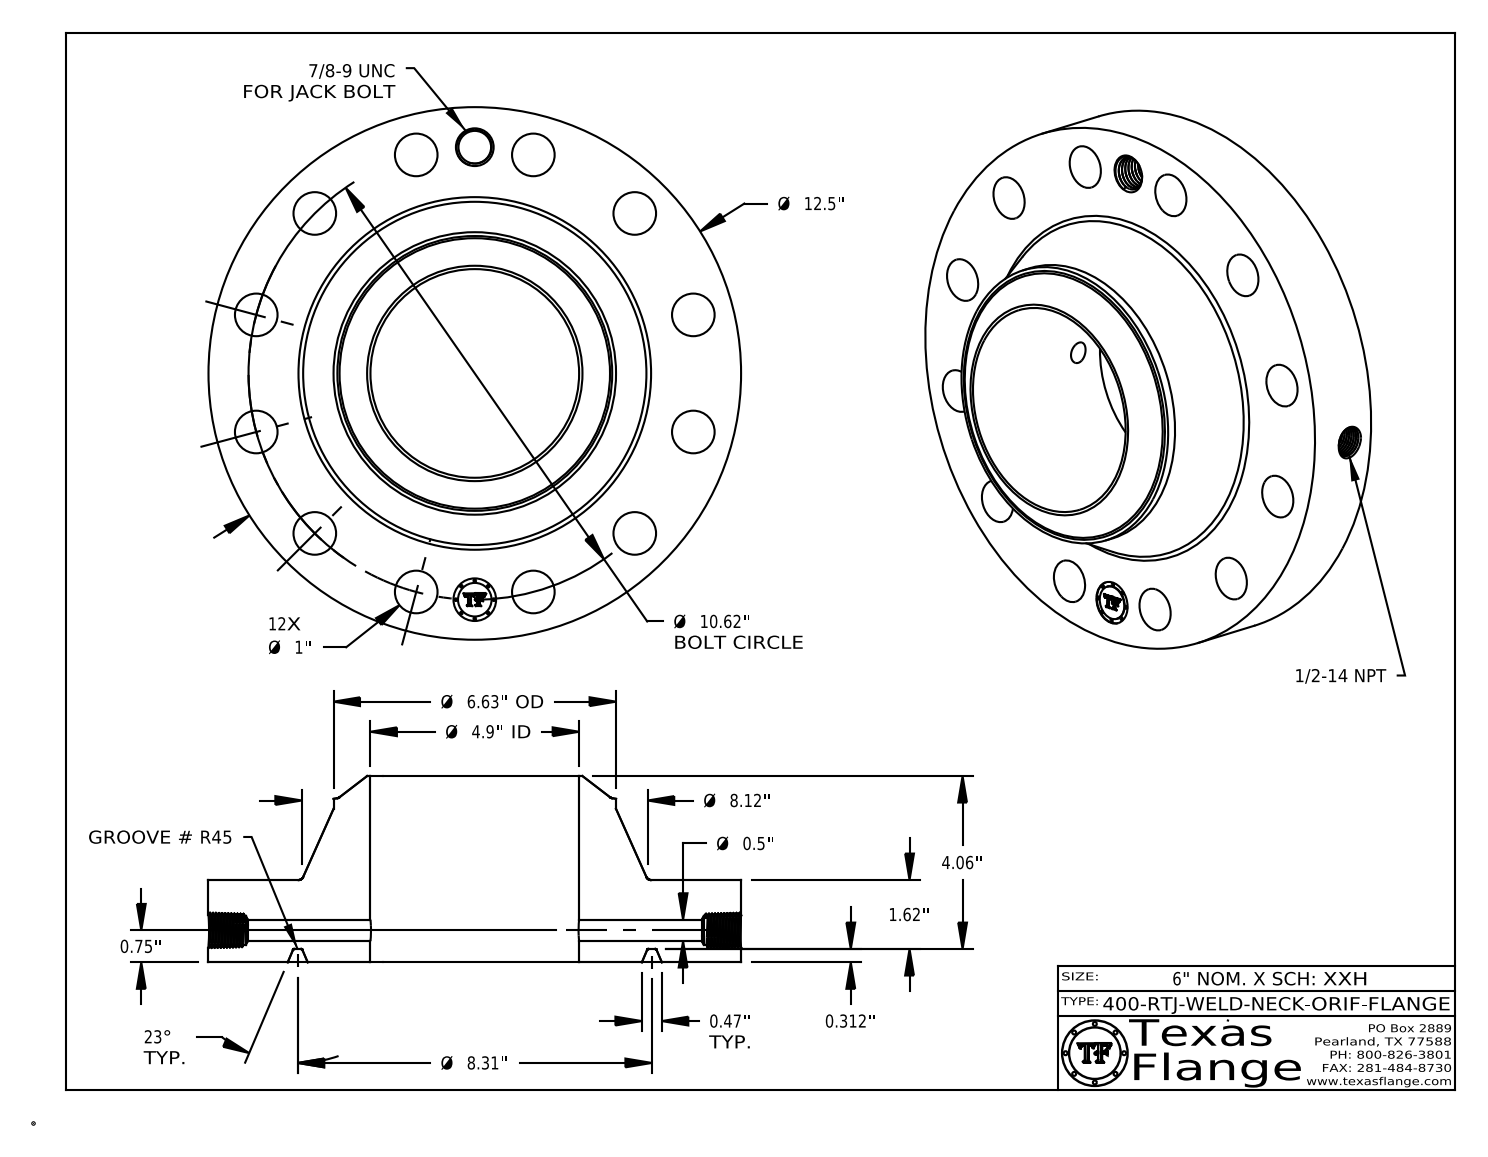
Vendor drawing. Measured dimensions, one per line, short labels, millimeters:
name: 400-RTJ-WELD-NECK
written by: CATIA V5 STEP AP214 (AUTOMOTIVE_DESIGN)
unit: mm
bodies: 1 solid, 800 faces (370 planar, 104 cylindrical, 326 other)
size: 317.5 × 317.5 × 111
volume: 3 681 000 mm³; area: 302 900 mm²
holes: 13× ⌀25.4, 1× ⌀12.7, 1× ⌀17.1, 1× ⌀19.5, 1× ⌀124.4
bosses: 8× ⌀1.5, 1× ⌀317.5, 1× ⌀168.4, 1× ⌀20
face distances: 49.1, 7.9, 41.1, 111, 103.1, 62, 0.4, 48.7, 40.8, 62.4
hole spacings: 134.9, 190.7, 233.6, 260.6, 134.9, 69.8, 269.7, 35.2
